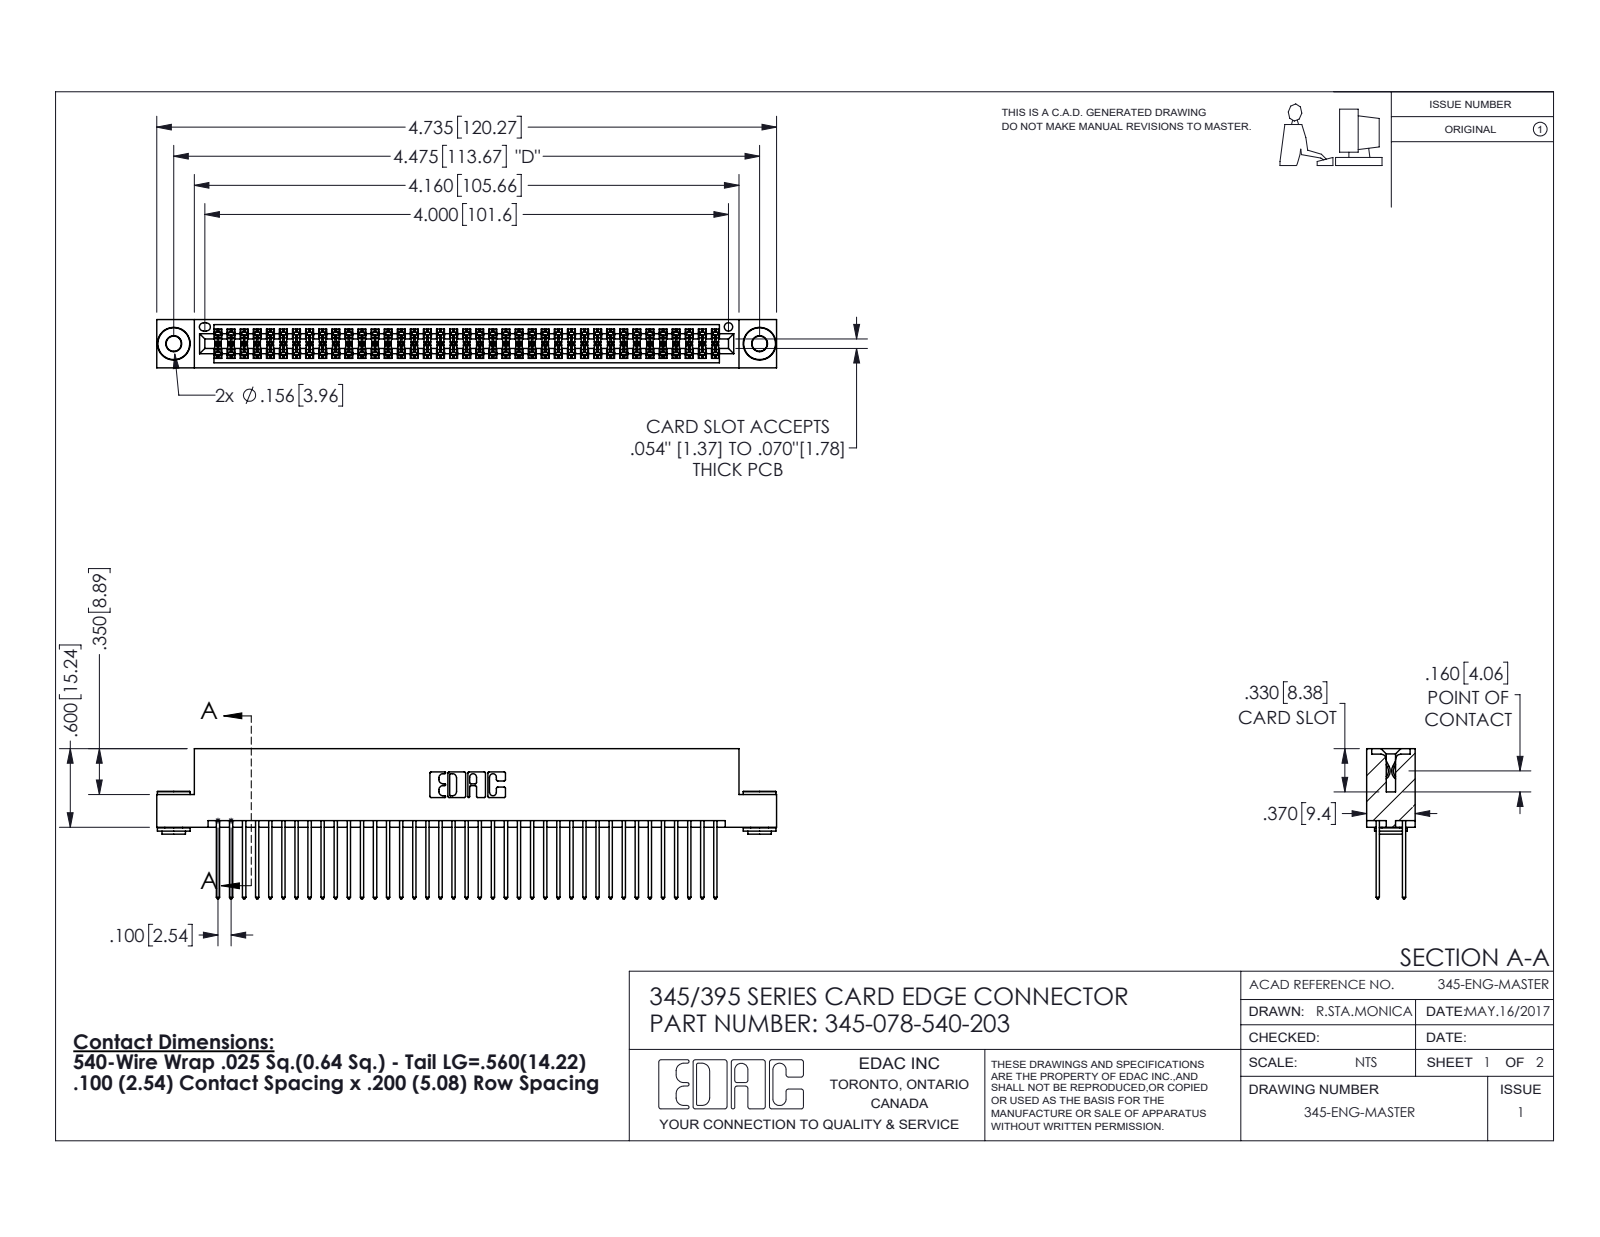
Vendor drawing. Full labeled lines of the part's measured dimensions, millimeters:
Part name (STEP PRODUCT): 345 Part_Flush Mounting Lugs - 0.156 Dia-TH; 345-250-002_345-250-002-102; 345-292-001_345-293-140; 345-078-540-203
STEP written by: SolidWorks 2016 (CONFIG_CONTROL_DESIGN)
Units: millimetres
Bodies: 81 solids, 4064 faces (2664 planar, 1392 cylindrical, 8 other)
Overall size (bounding box): 120.3 × 29.1 × 9.4
Volume: 12 000 mm³ · Surface area: 19 210 mm²
Round holes (diameter × count): ⌀2.9 ×2, ⌀4 ×2, ⌀1.6 ×1
Round bosses / shafts (diameter × count): ⌀6.4 ×2, ⌀4.6 ×2, ⌀3.5 ×2
Partial cylindrical surfaces — rounded edges, fillets, slot ends (radius × count): R0.2 ×117, R0.3 ×78, R0.3 ×22, R0.2 ×6, R0.8 ×6, R0.7 ×3, R0.4 ×2, R0.5 ×2
Main face-to-face distances: 1.8, 7.6, 5.1, 0.6, 2.5, 6.9, 9.4, 5.7, 4.4, 3.8
Hole centre spacings: 6.9, 107.7, 113.7
